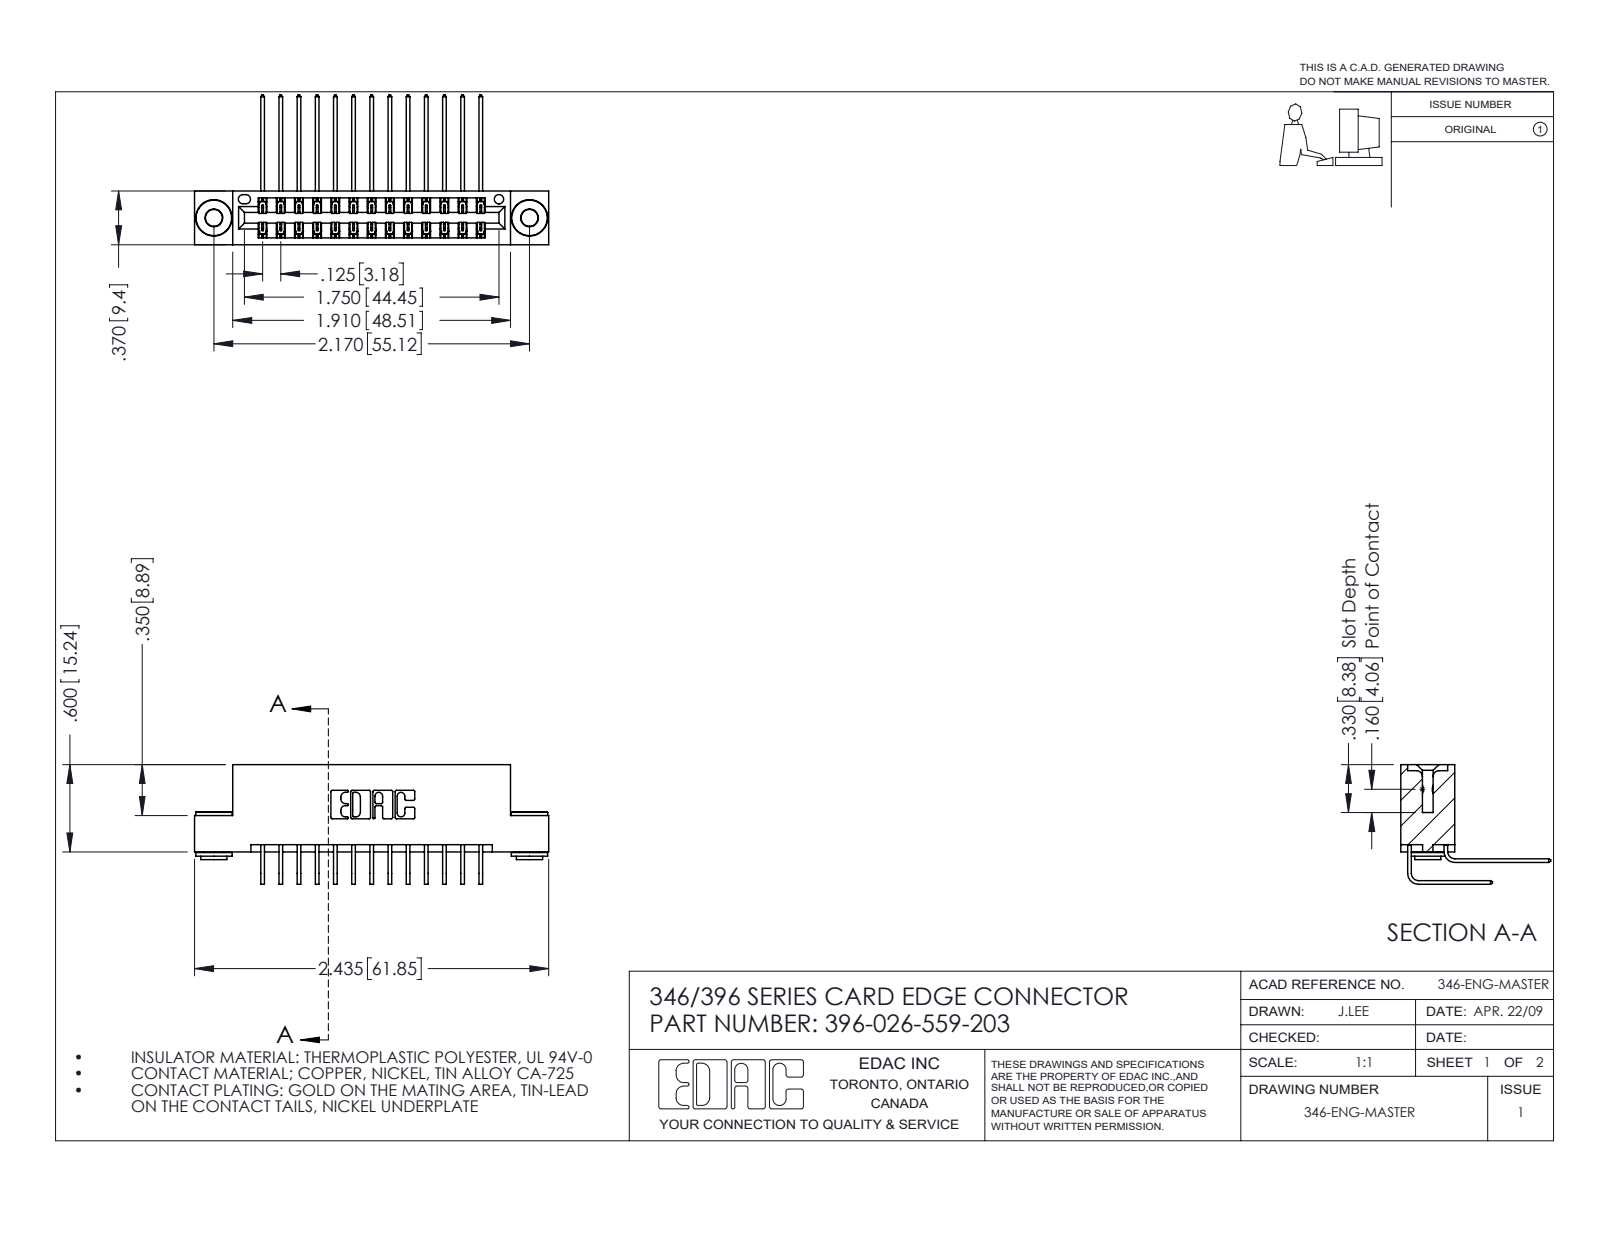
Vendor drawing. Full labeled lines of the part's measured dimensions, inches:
Part name (STEP PRODUCT): 396-026-559-203; 346 Part_Flush Mounting Lugs - 0.156 Dia-TH; 345-250-002_345-250-002-102; 345-292-001_558 559 Tail - 1 (+1 more)
STEP written by: SolidWorks 2016 (CONFIG_CONTROL_DESIGN)
Units: inches
Bodies: 29 solids, 1564 faces (1048 planar, 508 cylindrical, 8 other)
Overall size (bounding box): 2.435 × 1.03 × 0.823
Volume: 0.365 in³ · Surface area: 13.47 in²
Round holes (diameter × count): ⌀0.116 ×2, ⌀0.156 ×2, ⌀0.064 ×1
Round bosses / shafts (diameter × count): ⌀0.25 ×2, ⌀0.18 ×2, ⌀0.136 ×2
Partial cylindrical surfaces — rounded edges, fillets, slot ends (radius × count): R0.006 ×39, R0.01 ×22, R0.007 ×6, R0.031 ×6, R0.026 ×3, R0.014 ×2, R0.022 ×2, R0.024 ×2
Main face-to-face distances: 0.048, 0.322, 0.25, 0.025, 0.37, 0.298, 0.072, 0.275, 0.148, 0.222
Hole centre spacings: 0.246, 1.964, 2.17
